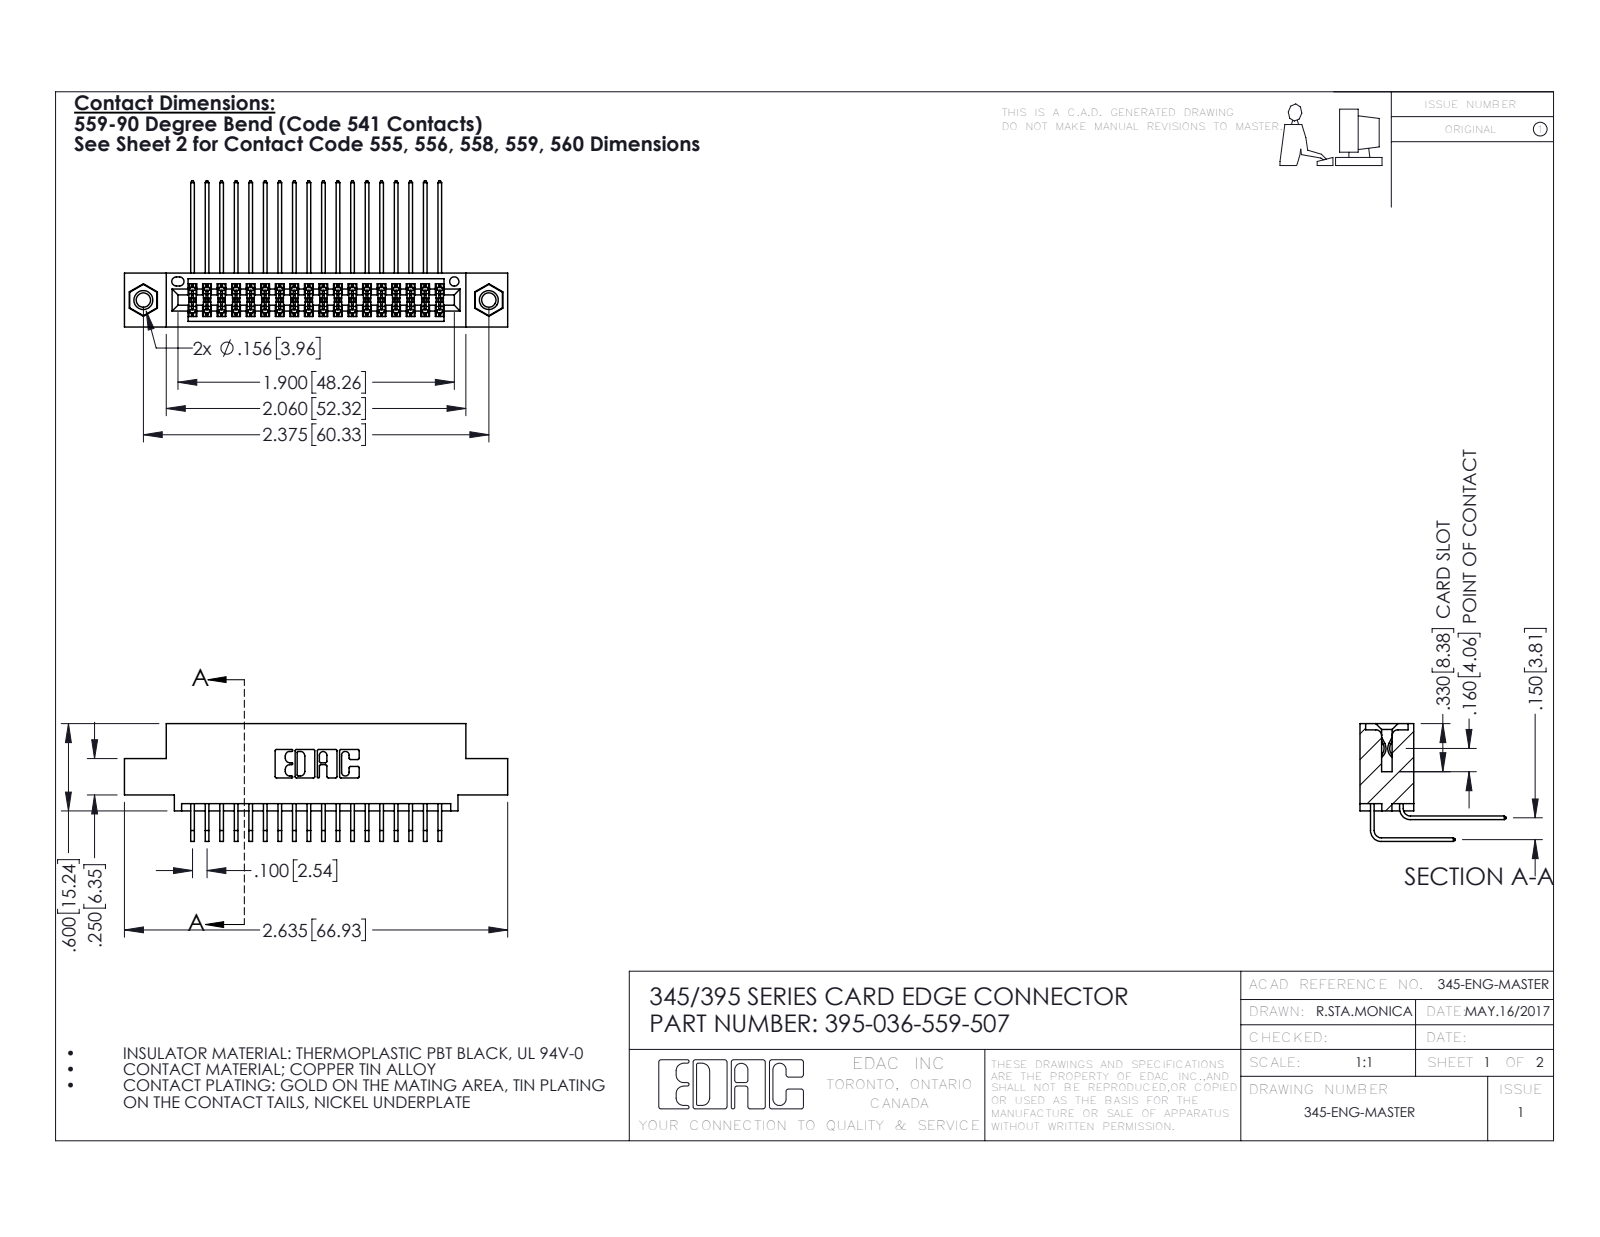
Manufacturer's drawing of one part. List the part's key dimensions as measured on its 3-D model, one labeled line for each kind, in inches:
Part name (STEP PRODUCT): 345 Part_0.110 Offset - 0.156 Dia-TI; 345-292-001_558 559 Tail - 1; 345-292-001_559 Tail - 2; 345-250-001_345-250-005-103 (+1 more)
STEP written by: SolidWorks 2016 (CONFIG_CONTROL_DESIGN)
Units: inches
Bodies: 39 solids, 2062 faces (1376 planar, 670 cylindrical, 16 other)
Overall size (bounding box): 2.635 × 1.005 × 0.809
Volume: 0.391 in³ · Surface area: 15.64 in²
Round holes (diameter × count): ⌀0.098 ×2, ⌀0.125 ×2, ⌀0.156 ×2, ⌀0.064 ×1
Round bosses / shafts (diameter × count): ⌀0.155 ×2
Partial cylindrical surfaces — rounded edges, fillets, slot ends (radius × count): R0.006 ×54, R0.01 ×22, R0.007 ×6, R0.031 ×6, R0.026 ×3, R0.014 ×2, R0.019 ×2, R0.022 ×2
Main face-to-face distances: 0.072, 0.298, 0.2, 0.37, 0.098, 0.272, 0.025, 0.225, 0.15, 0.175
Hole centre spacings: 0.27, 2.141, 2.375
